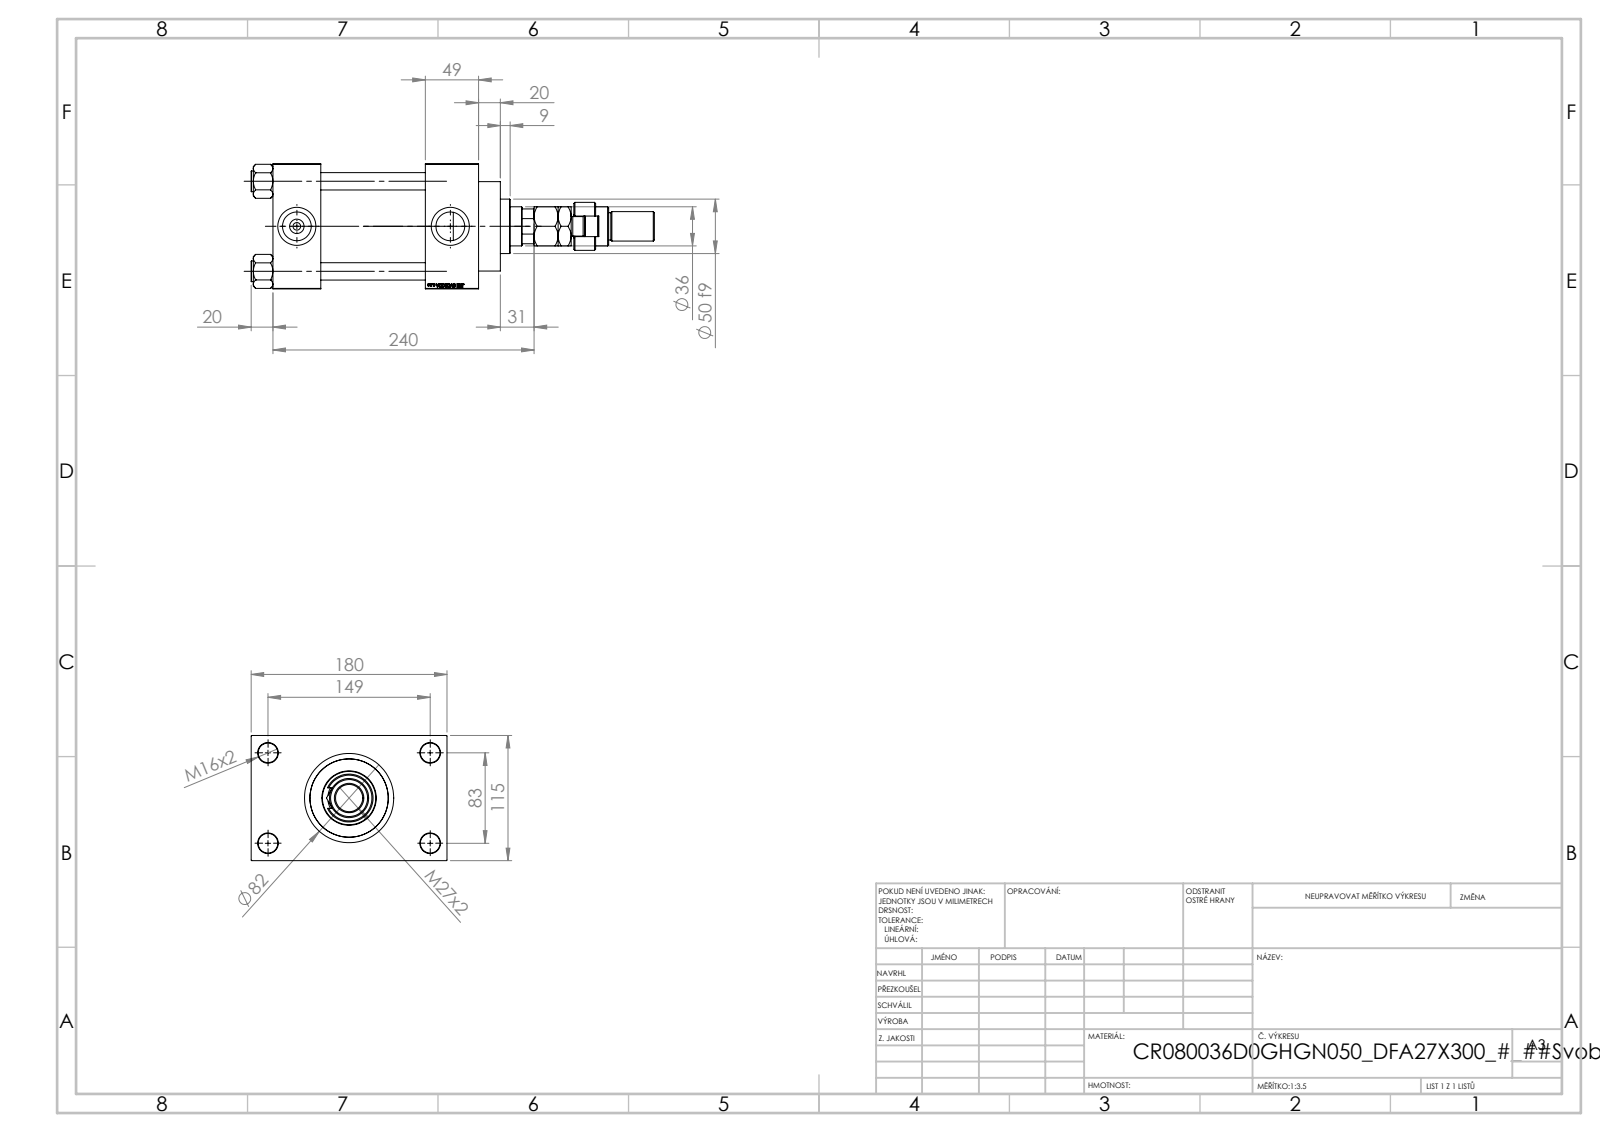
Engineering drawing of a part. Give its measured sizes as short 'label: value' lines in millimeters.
name: V215CR_D_TYCINKA; V215_VC_A; V215CR_VCP_D; NUT_M5_D (+3 more)
written by: SolidWorks 2019 (CONFIG_CONTROL_DESIGN)
unit: mm
bodies: 13 solids, 1236 faces (573 planar, 101 cylindrical, 562 other)
size: 370.5 × 180 × 115
volume: 2 156 000 mm³; area: 342 783 mm²
holes: 4× ⌀16, 4× ⌀18, 2× ⌀7, 2× ⌀26.44, 2× ⌀35, 1× ⌀25.5, 1× ⌀39, 1× ⌀61, 1× ⌀72, 1× ⌀80
bosses: 4× ⌀19, 1× ⌀86, 1× ⌀82, 1× ⌀50, 1× ⌀44, 1× ⌀36, 1× ⌀28, 1× ⌀27
rounds: 1× R9.5, 1× R15, 1× R17.5
face distances: 115, 96, 145, 49, 44, 140, 189, 32.5, 147.5, 209
hole spacings: 33.15, 58.48, 82.7, 85.28, 89.24, 115.85, 142.43, 83
